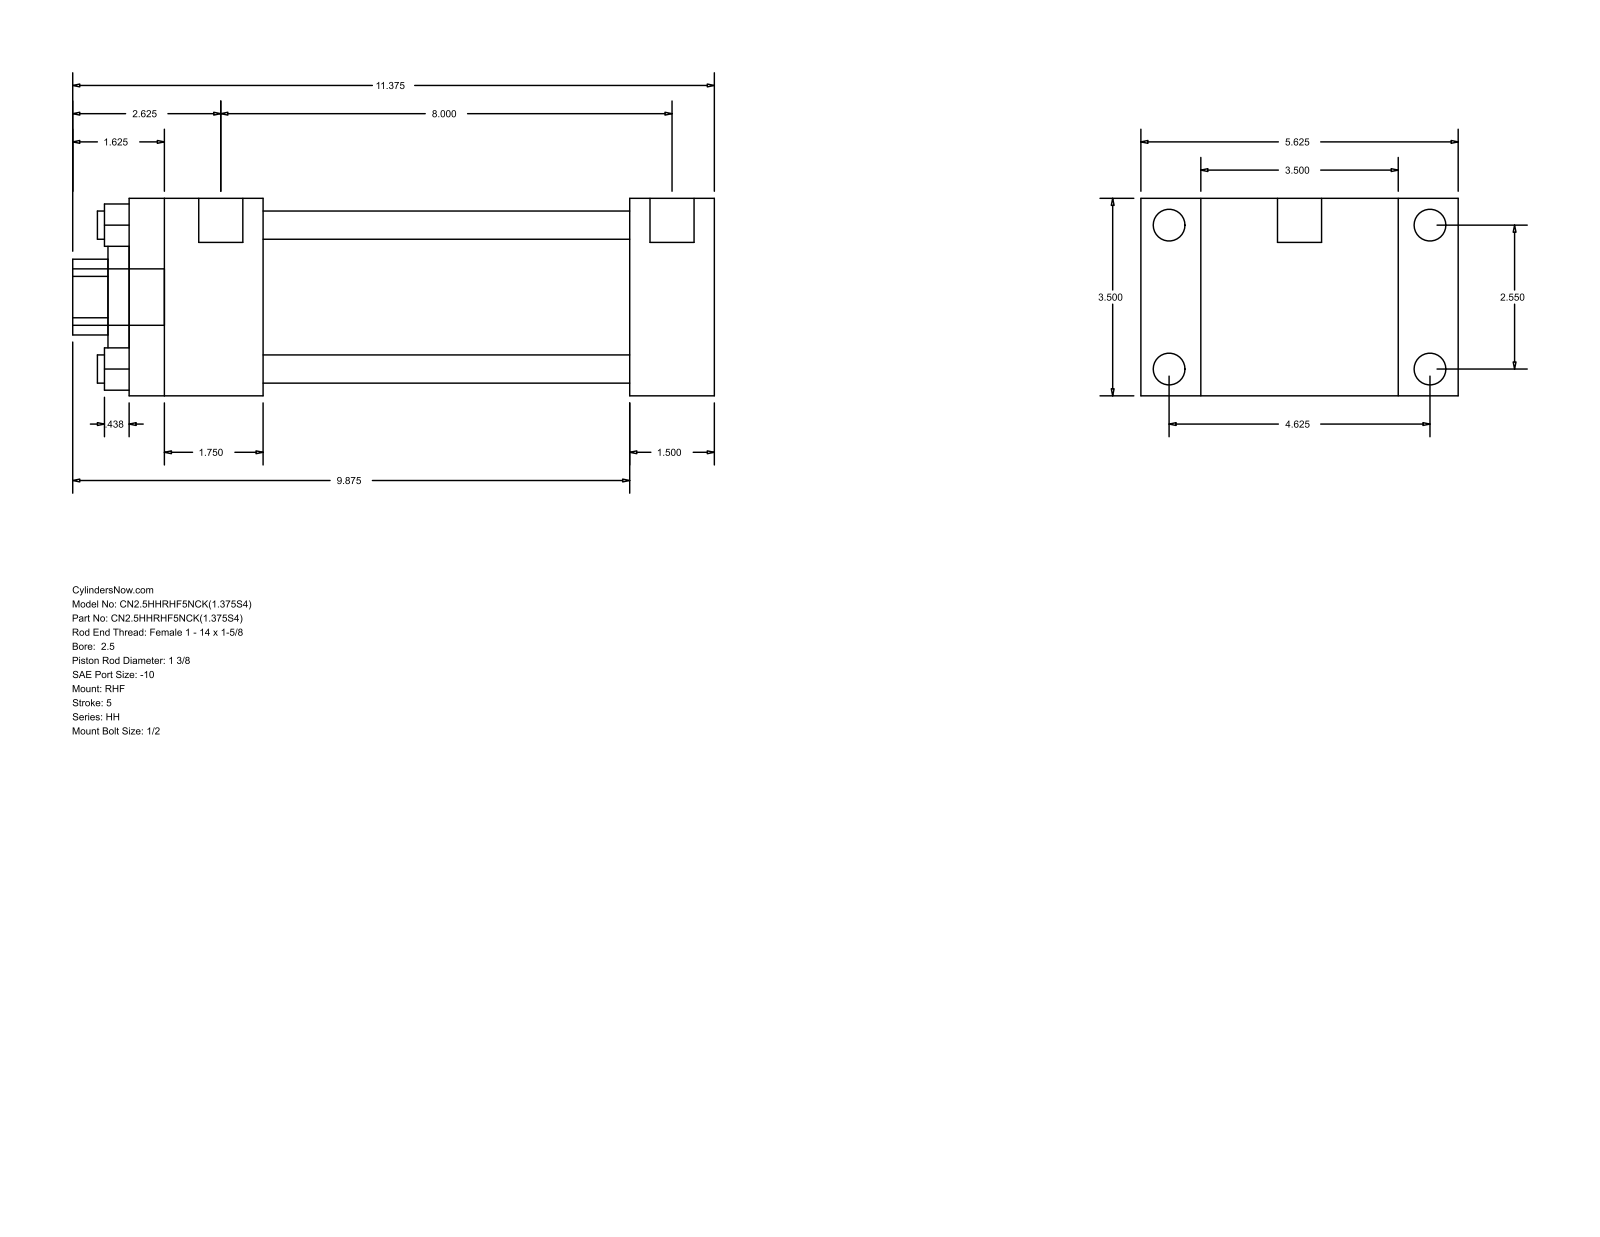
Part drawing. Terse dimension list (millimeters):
name: HH_RHF__0250_1.375
written by: GSSL Pune (CONFIG_CONTROL_DESIGN)
unit: mm
bodies: 0 solids, 88 faces (60 planar, 28 cylindrical, 0 other)
size: 288.93 × 142.88 × 88.9
holes: 4× ⌀12.7, 1× ⌀34.92, 1× ⌀50.8, 1× ⌀73.03
bosses: 4× ⌀14.3, 4× ⌀5.56, 2× ⌀19.84, 1× ⌀25.4
rounds: 1× R17.06
face distances: 88.9, 38.11, 26.99, 115.89, 225.42, 263.53, 142.88, 60.32, 165.1, 203.21
hole spacings: 45.79, 64.76, 91.58
